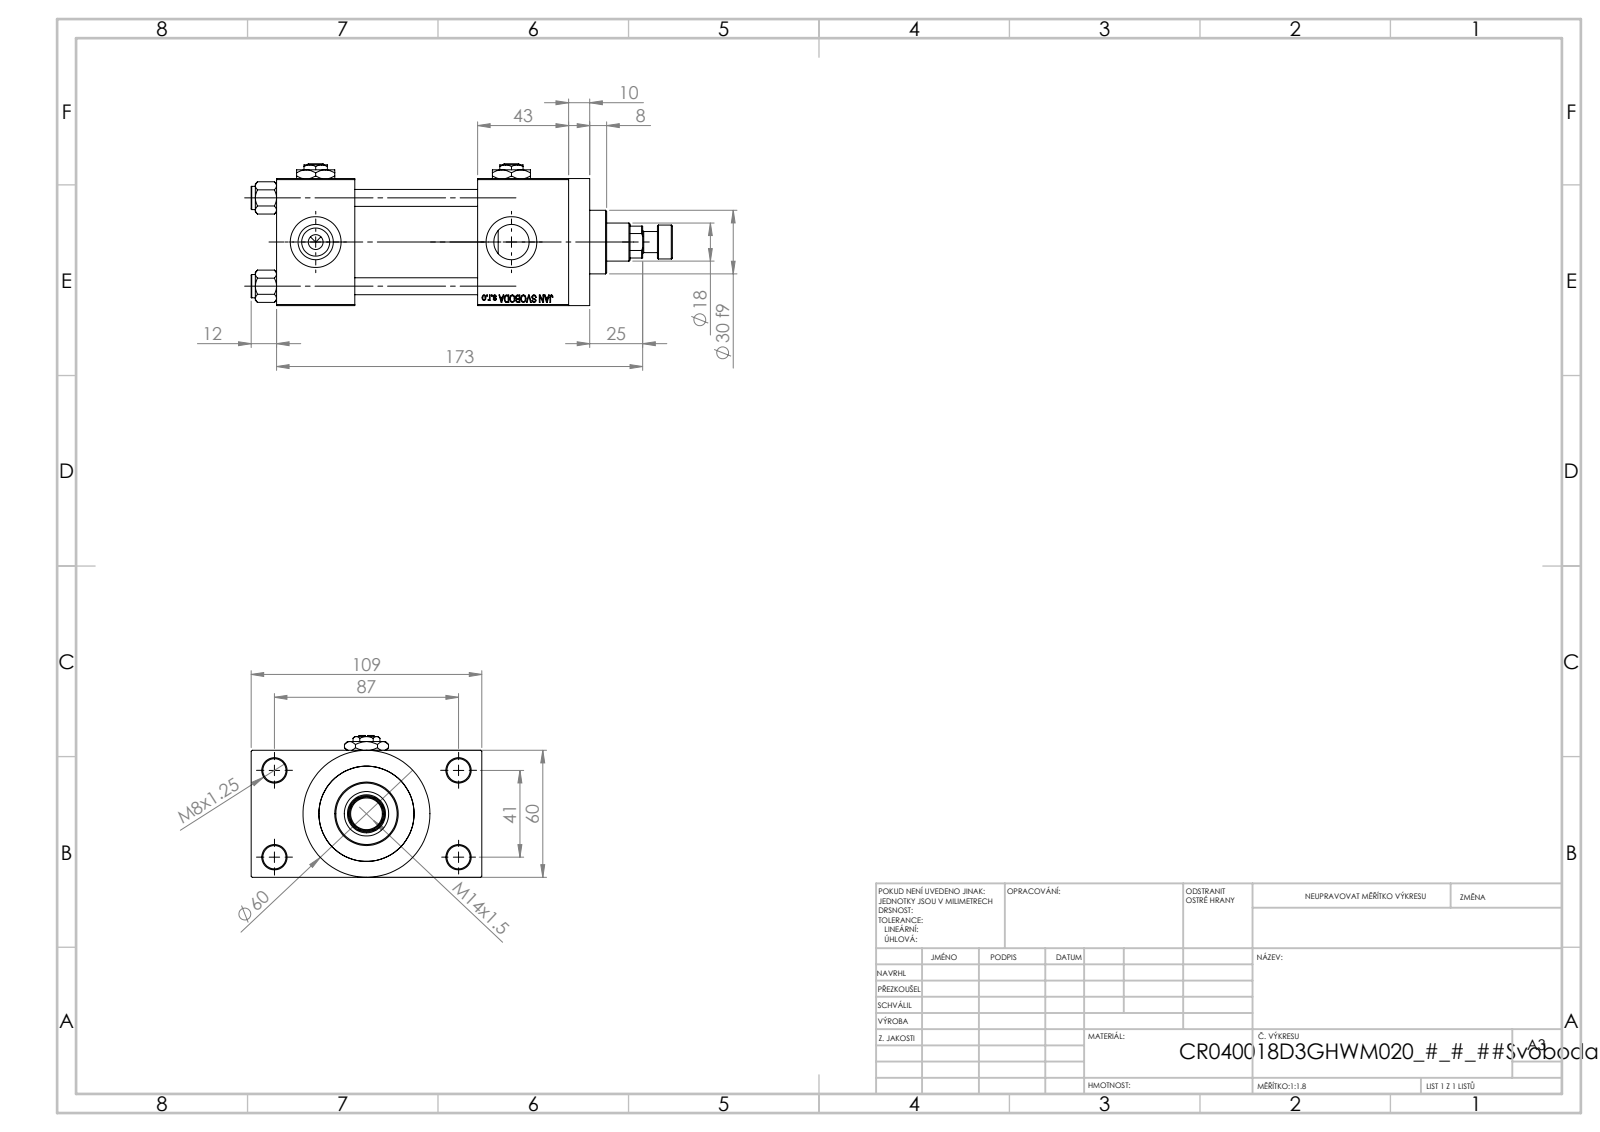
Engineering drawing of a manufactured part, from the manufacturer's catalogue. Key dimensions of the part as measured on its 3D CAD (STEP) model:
Part name (STEP PRODUCT): V215CR_ROD_END_W; Zatka_pro_OIL_PORT; NUT_M5_D; V215CR_VCP_D (+3 more)
STEP written by: SolidWorks 2019 (CONFIG_CONTROL_DESIGN)
Units: millimetres
Bodies: 14 solids, 1218 faces (549 planar, 103 cylindrical, 566 other)
Overall size (bounding box): 199 × 109 × 67
Volume: 512 293 mm³ · Surface area: 126 168 mm²
Round holes (diameter × count): ⌀8 ×4, ⌀11 ×4, ⌀16.66 ×4, ⌀24 ×4, ⌀7 ×3, ⌀8.5 ×1, ⌀18 ×1, ⌀21 ×1, ⌀31 ×1, ⌀40 ×1, ⌀45 ×1
Round bosses / shafts (diameter × count): ⌀11 ×4, ⌀60 ×1, ⌀46 ×1, ⌀30 ×1, ⌀16 ×1, ⌀10 ×1
Partial cylindrical surfaces — rounded edges, fillets, slot ends (radius × count): R8.5 ×1
Main face-to-face distances: 60, 24.5, 58, 84.5, 37, 95, 43, 138, 101, 10
Hole centre spacings: 22.65, 29.49, 41.7, 47.15, 48.09, 64.35, 76.49, 41
